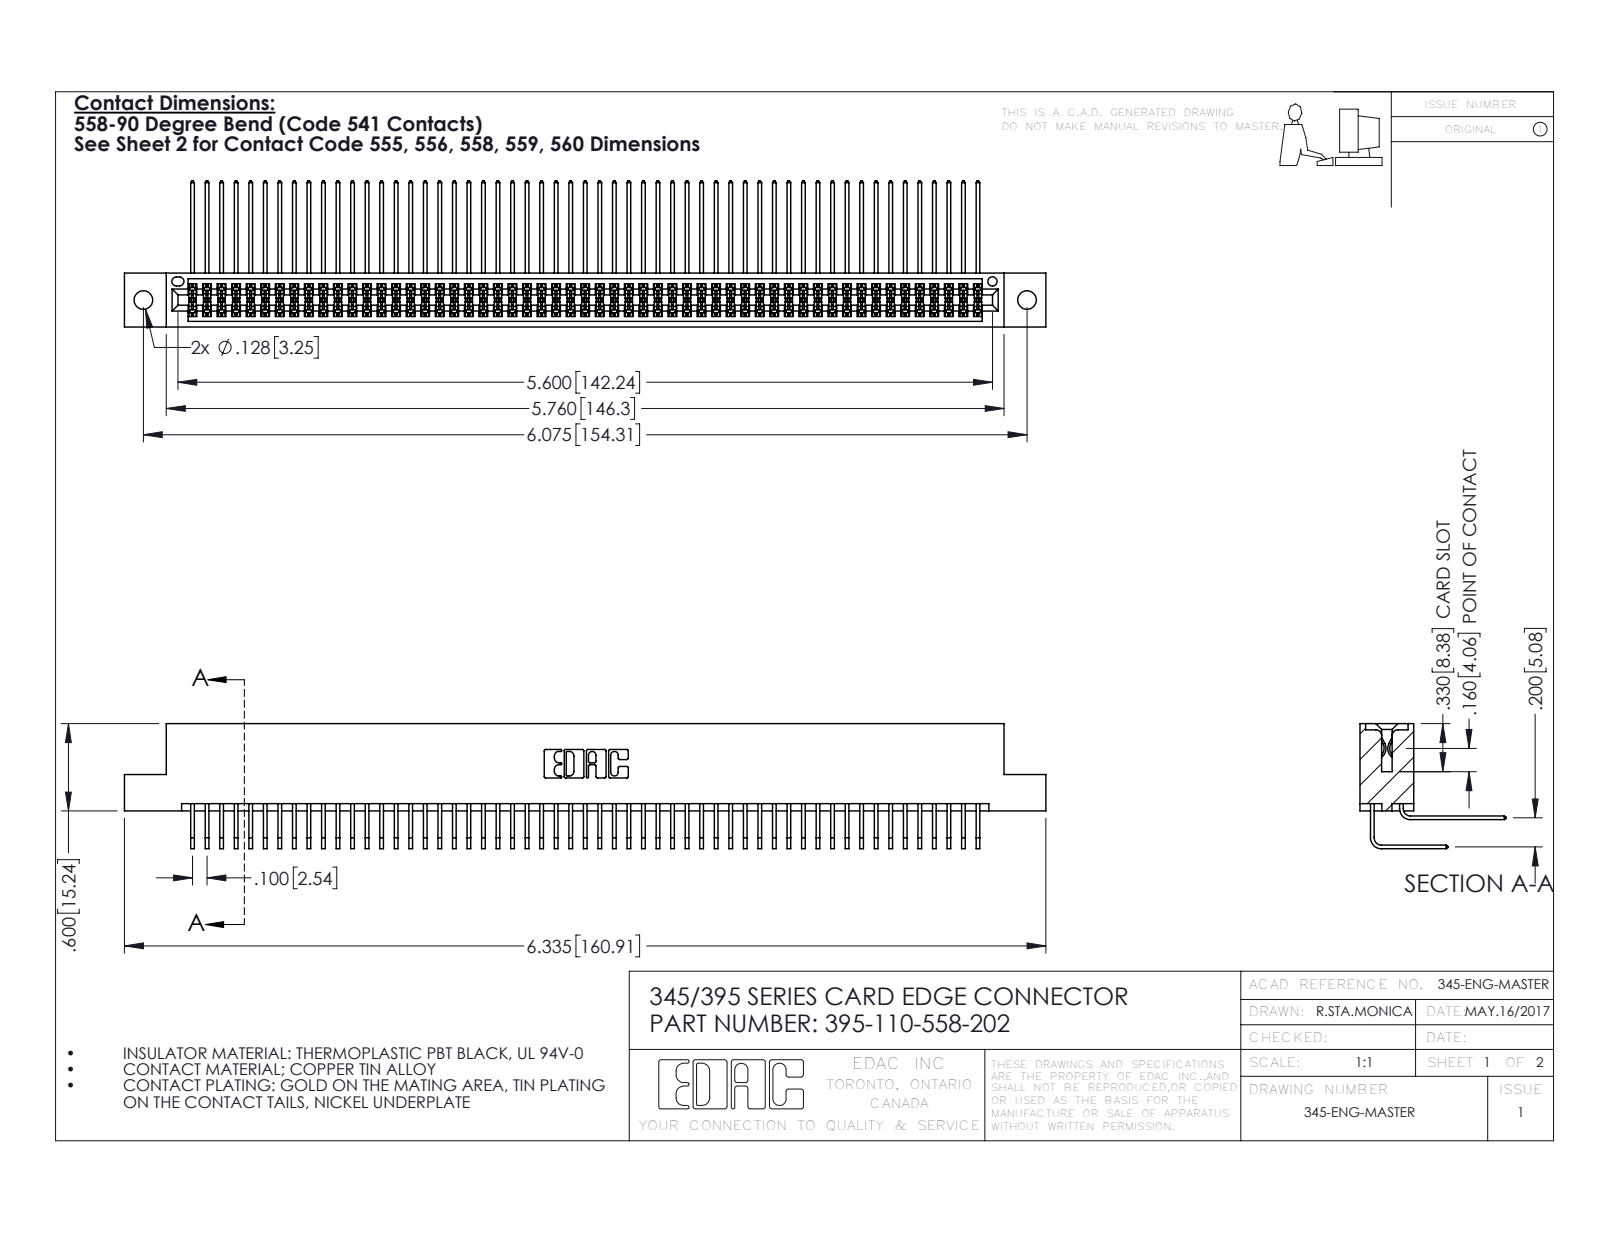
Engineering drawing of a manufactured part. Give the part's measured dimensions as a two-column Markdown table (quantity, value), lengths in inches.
| quantity | value |
| --- | --- |
| part name | 345 Part_Flush Mounting Lugs - 0.128 Dia; 345-292-001_558 559 Tail - 1; 345-292-001_558 Tail - 2; 395-110-558-202 |
| STEP written by | SolidWorks 2016 (CONFIG_CONTROL_DESIGN) |
| units | inches |
| bodies | 111 solids, 5846 faces (3930 planar, 1916 cylindrical, 0 other) |
| overall size | 6.335 × 1.005 × 0.859 |
| volume | 0.998 in³ |
| surface area | 42.05 in² |
| round holes (diameter × count) | 0.128 × 2, 0.064 × 1 |
| partial cylindrical surfaces (radius × count) | 0.006 × 166, 0.01 × 22, 0.007 × 6, 0.031 × 6, 0.026 × 3, 0.014 × 2, 0.019 × 2, 0.022 × 2 |
| main face-to-face distances | 0.072, 0.298, 0.2, 0.37, 0.098, 0.272, 0.025, 0.225, 0.025, 0.175 |
| hole center spacings | 0.27, 5.839, 6.075 |
